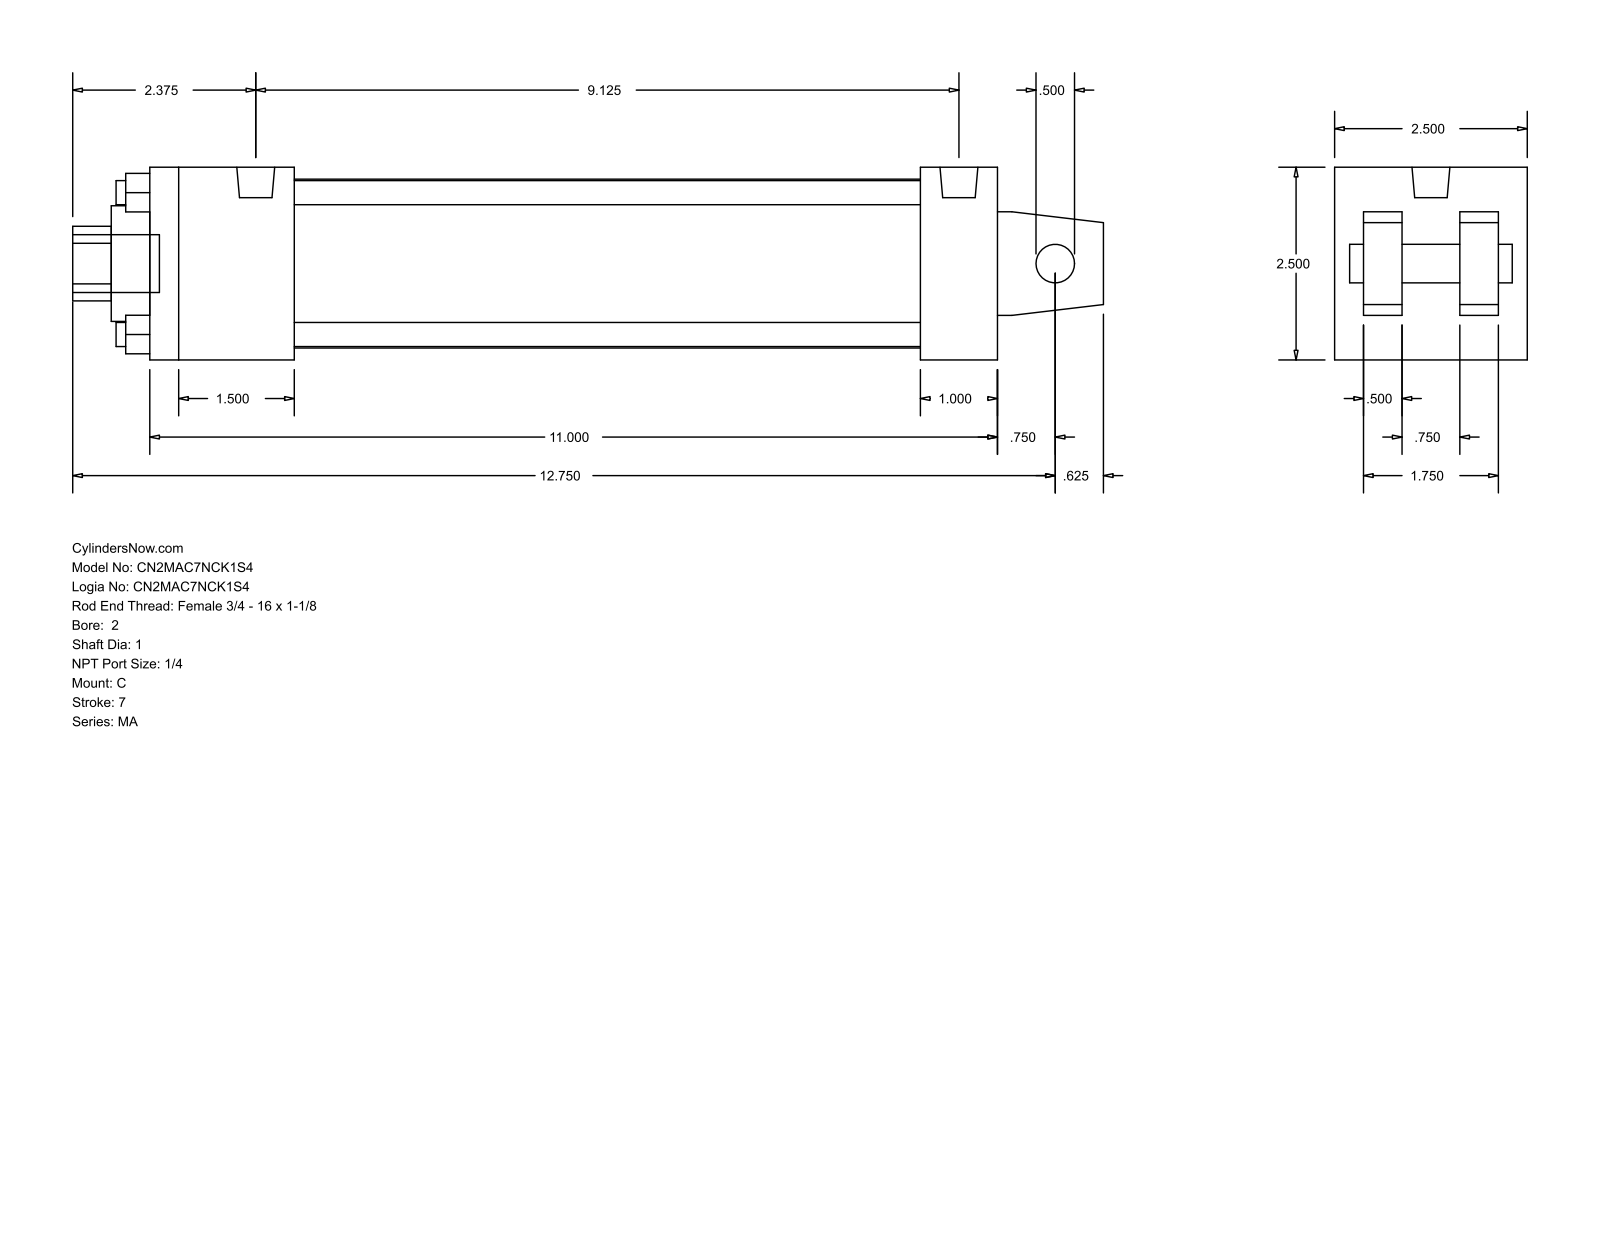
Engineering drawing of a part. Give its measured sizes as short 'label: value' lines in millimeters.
name: MA_C__0200_1
written by: GSSL Pune (CONFIG_CONTROL_DESIGN)
unit: mm
bodies: 0 solids, 103 faces (76 planar, 27 cylindrical, 0 other)
size: 339.73 × 63.5 × 63.5
holes: 4× ⌀7.94, 1× ⌀12.7, 1× ⌀25.4, 1× ⌀38.1, 1× ⌀55.63
bosses: 4× ⌀7.94, 2× ⌀12.49, 1× ⌀19.05
rounds: 1× R12.29
face distances: 63.5, 12.7, 279.4, 22.22, 41.28, 9.52, 53.98, 31.76, 47.63, 25.4
hole spacings: 33.05, 46.74, 66.1
